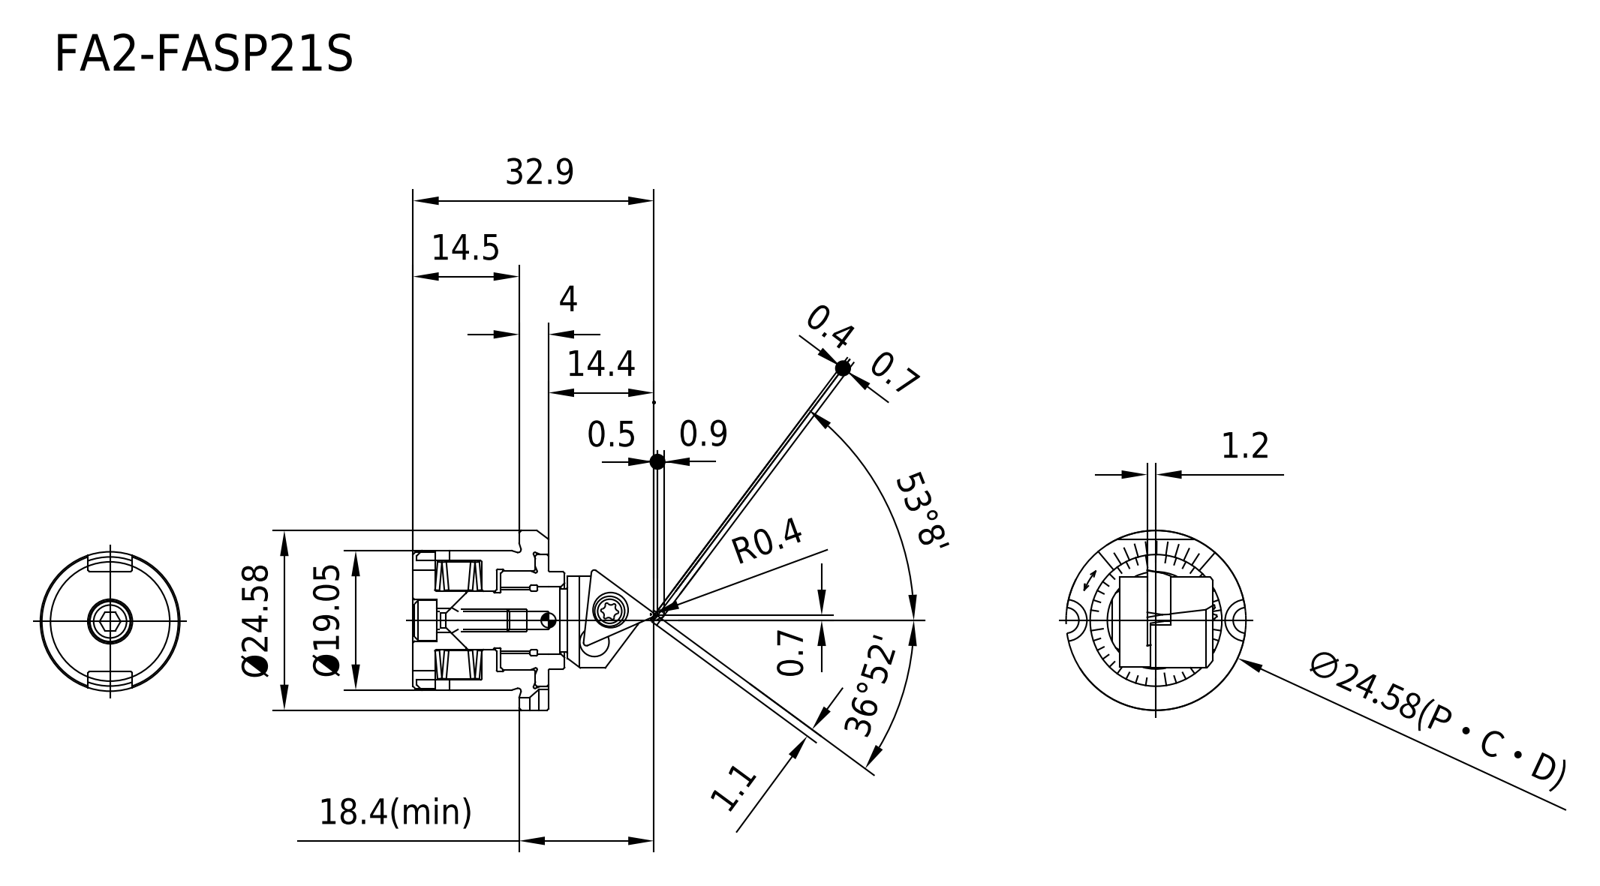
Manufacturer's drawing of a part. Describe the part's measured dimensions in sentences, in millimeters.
The part is named "FA2-FASP21S_ASM". Its 3-D file was written by "SIEMENS PLM Software NX 10.0 (AUTOMOTIVE_DESIGN)". It is 14 solids with 927 faces: 670 planar, 94 cylindrical and 163 other. Overall it measures 31.65 by 24.58 by 24.32 millimeters. Its volume is 6 298 cubic millimeters and its surface area 8 600 square millimeters. Round holes: 2 of diameter 2.5, 1 of diameter 3.2, 1 of diameter 4, 1 of diameter 5.9, 1 of diameter 8.58, 1 of diameter 9.2, 1 of diameter 9.7, 1 of diameter 13.5, 1 of diameter 14, 1 of diameter 16.3, 1 of diameter 18.1. Round bosses or shafts: 2 of diameter 3, 1 of diameter 24.58, 1 of diameter 19.05, 1 of diameter 18, 1 of diameter 8.89, 1 of diameter 8.7, 1 of diameter 8, 1 of diameter 7.5. Partial cylindrical surfaces (rounded edges, fillets, slot ends): 7 of radius 0.2, 6 of radius 0.22, 6 of radius 0.47, 3 of radius 0.4, 2 of radius 1.8, 2 of radius 2.88, 1 of radius 6.65, 1 of radius 9.35. The main face-to-face distances are 3, 2, 6.4, 9.1, 18.5, 15.5, 1.8, 9.4, 13.7, 4. The hole center spacings are 4.87.
